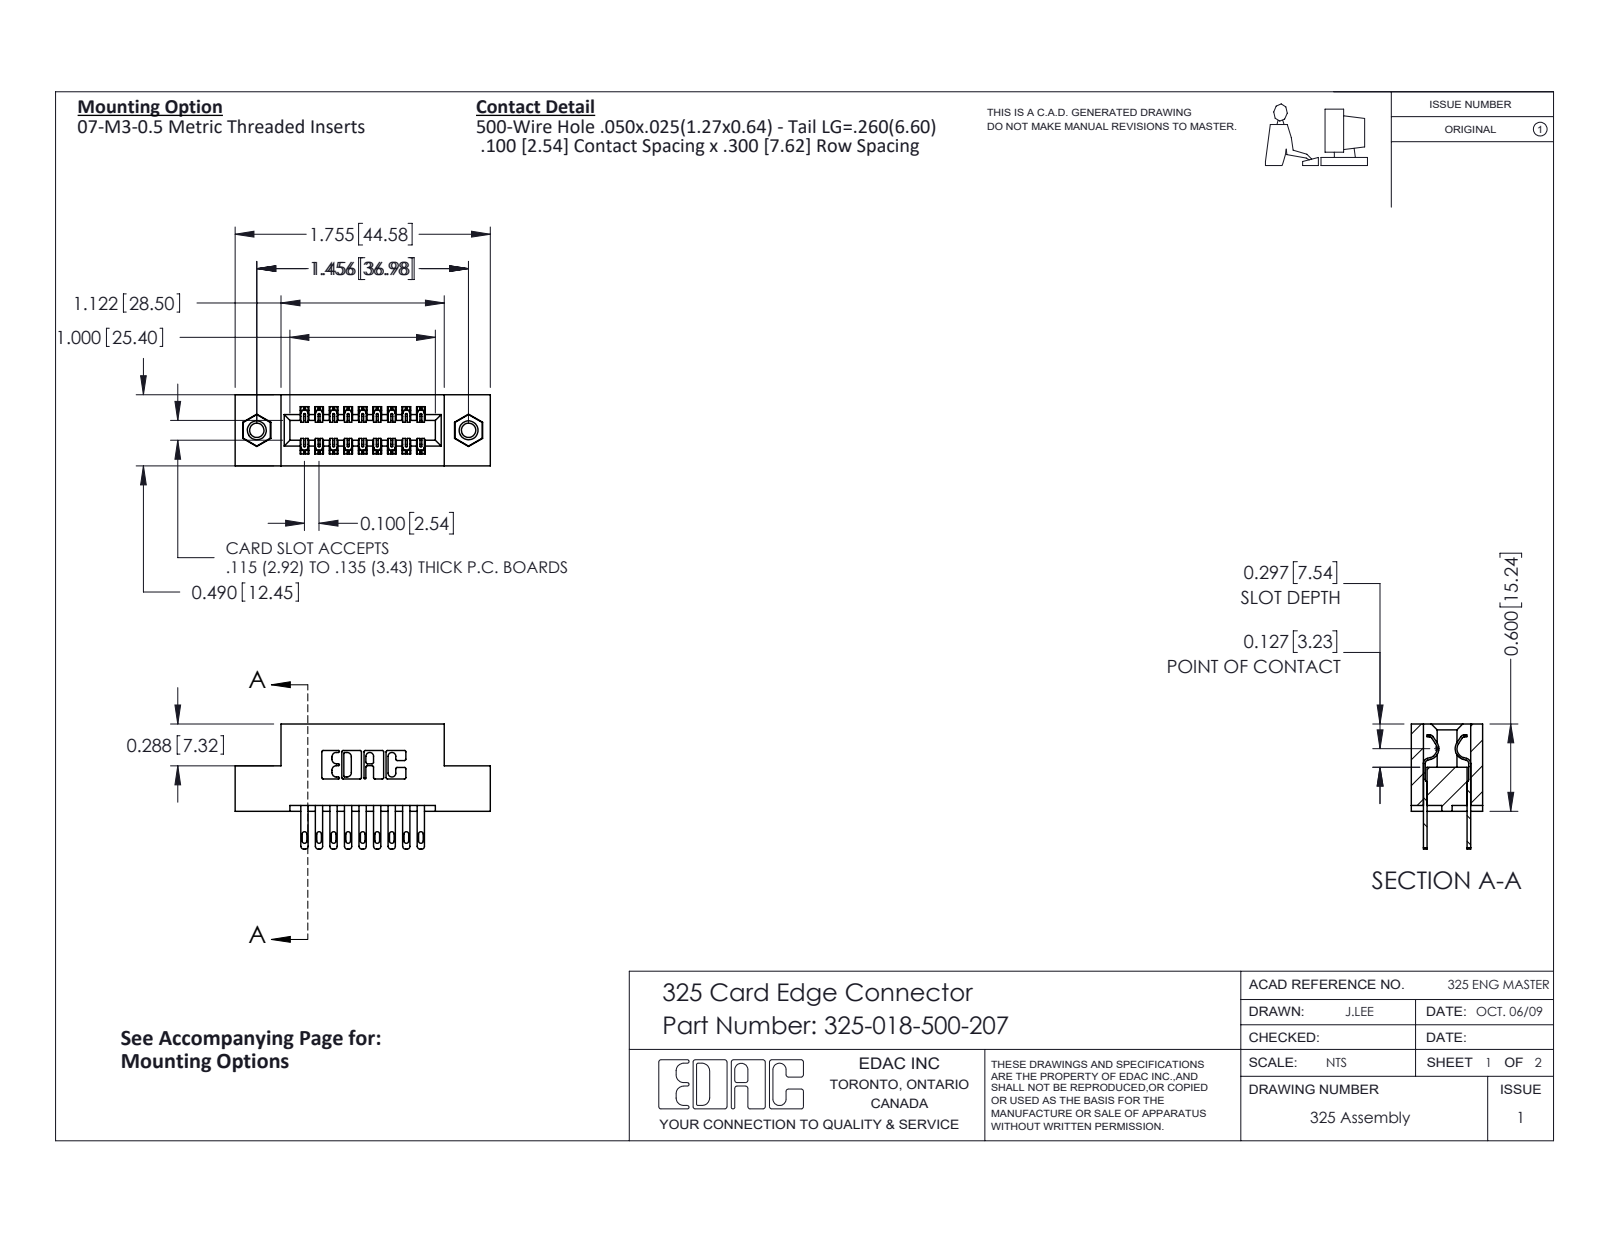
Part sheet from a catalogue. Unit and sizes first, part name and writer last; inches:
Units: inches
Overall size (bounding box): 1.755 × 0.86 × 0.49
Round holes (diameter × count): ⌀0.098 ×2, ⌀0.125 ×2, ⌀0.16 ×2
Round bosses / shafts (diameter × count): ⌀0.155 ×2
Partial cylindrical surfaces — rounded edges, fillets, slot ends (radius × count): R0.006 ×27, R0.01 ×22, R0.016 ×18, R0.02 ×18, R0.007 ×6, R0.031 ×6, R0.026 ×3, R0.014 ×2
Main face-to-face distances: 0.3, 0.083, 0.407, 0.04, 0.1, 0.49, 0.2, 0.107, 0.383, 0.025
Hole centre spacings: 1.456
Volume: 0.336 in³ · Surface area: 9.438 in²
Bodies: 21 solids, 1038 faces (642 planar, 380 cylindrical, 16 other)
Part name (STEP PRODUCT): 345-250-001_345-250-005-103; 325 Part_TI; 325-292-001_325-293-100; 325-018-500-207
STEP written by: SolidWorks 2016 (CONFIG_CONTROL_DESIGN)
